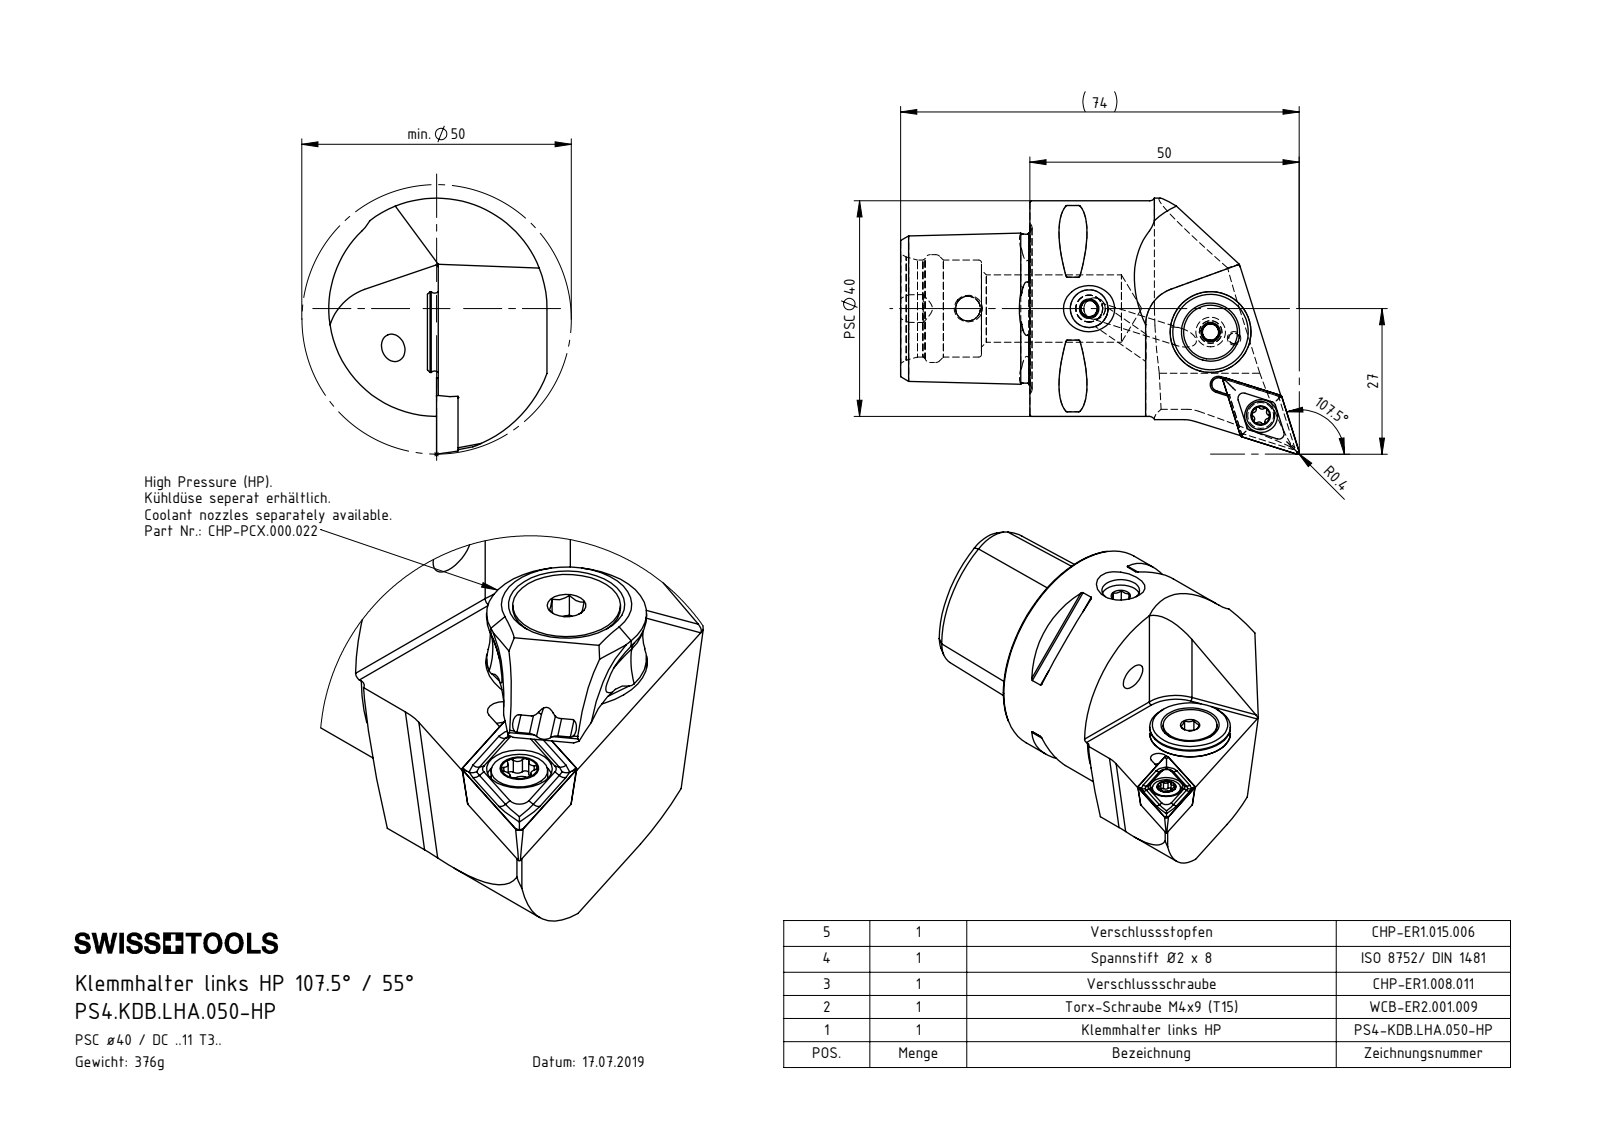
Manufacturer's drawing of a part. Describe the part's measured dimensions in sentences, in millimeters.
The part is named "CHP-ER1.015.006; ISO 8752 2x8; DCMT11T304; DIN 7991 - M5x15 (+6 more)". Its 3-D file was written by "SolidWorks 2017 (AUTOMOTIVE_DESIGN)". It is 8 solids with 387 faces: 91 planar, 100 cylindrical and 196 other. Overall it measures 74.01 by 47.5 by 40.5 millimeters. Its volume is 47 579 cubic millimeters and its surface area 15 103 square millimeters. Round holes: 2 of diameter 3.3, 2 of diameter 4.2, 1 of diameter 1.2, 1 of diameter 2, 1 of diameter 2.5, 1 of diameter 3, 1 of diameter 4, 1 of diameter 4.4, 1 of diameter 4.6, 1 of diameter 5, 1 of diameter 5.2, 1 of diameter 6.1. Round bosses or shafts: 1 of diameter 40, 1 of diameter 15, 1 of diameter 13.4, 1 of diameter 10, 1 of diameter 8, 1 of diameter 5.5, 1 of diameter 5.25, 1 of diameter 5. Partial cylindrical surfaces (rounded edges, fillets, slot ends): 8 of radius 0.3, 6 of radius 0.34, 6 of radius 0.59, 2 of radius 0.5, 2 of radius 7, 1 of radius 1.25, 1 of radius 3, 1 of radius 20.5. The main face-to-face distances are 4.5, 21.5, 15.7, 20.2, 24, 45.5, 16.53, 0.83, 3.67, 15.52. The hole center spacings are 1, 4.5, 15.15, 15.26, 18.05, 18.18, 21.97, 22.5.
